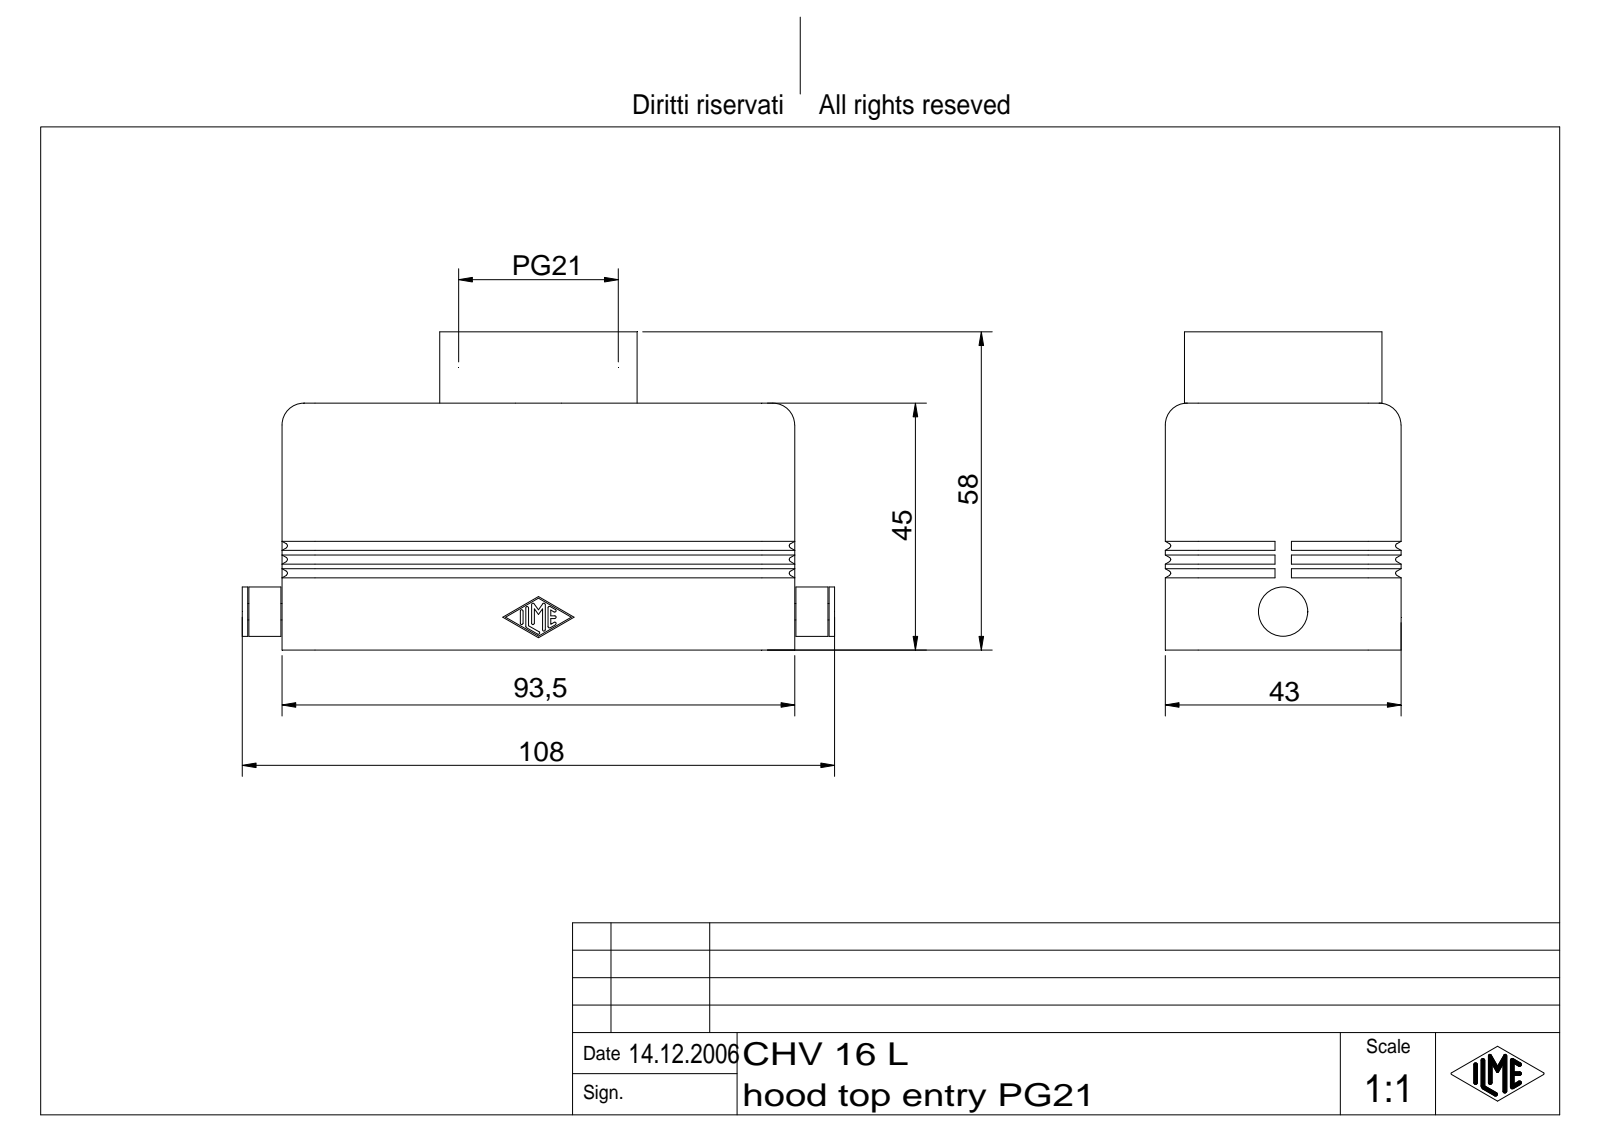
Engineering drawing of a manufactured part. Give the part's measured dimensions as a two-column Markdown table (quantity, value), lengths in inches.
| quantity | value |
| --- | --- |
| part name | CHV 16 L |
| STEP written by | Autodesk Inventor 7 (AUTOMOTIVE_DESIGN) |
| units | inches |
| bodies | 1 solid, 401 faces (108 planar, 162 cylindrical, 131 other) |
| overall size | 4.252 × 2.283 × 1.693 |
| volume | 3.457 in³ |
| surface area | 52.3 in² |
| round holes (diameter × count) | 0.827 × 1, 1.054 × 1 |
| round bosses / shafts (diameter × count) | 1.417 × 1, 0.354 × 1, 0.118 × 1 |
| partial cylindrical surfaces (radius × count) | 0.016 × 24, 0.01 × 14, 0.059 × 4, 0.118 × 4, 0.157 × 4, 0.236 × 4, 0.197 × 2 |
| main face-to-face distances | 0.118, 1.575, 1.457, 1.693, 3.563, 3.681, 3.445, 0.325, 0.443, 3.238 |
